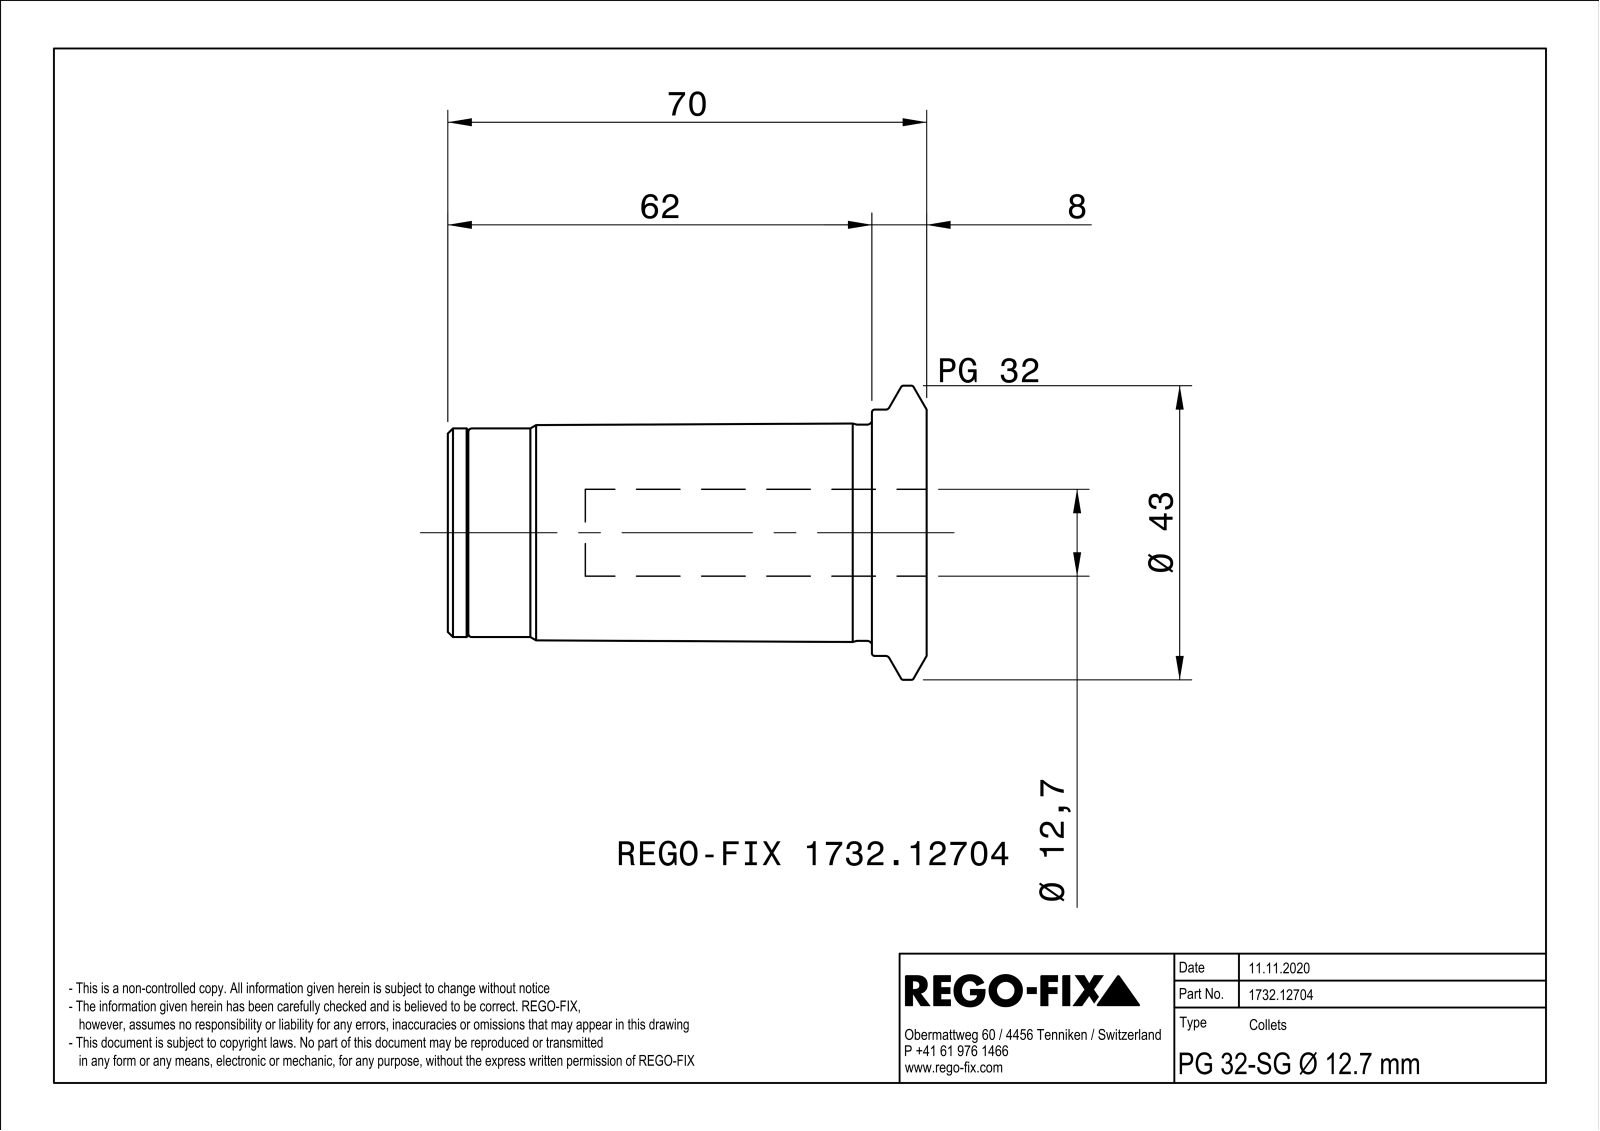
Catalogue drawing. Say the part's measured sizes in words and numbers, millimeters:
The part is named "NOCUT". Its 3-D file was written by "SIEMENS PLM Software Solid Edge ST10 (AUTOMOTIVE_DESIGN)". It is 1 solid with 127 faces: 31 planar, 41 cylindrical and 55 other. Overall it measures 70 by 43 by 42.99 millimeters. Its volume is 45 037 cubic millimeters and its surface area 16 567 square millimeters. Round holes: 3 of diameter 4, 1 of diameter 8.92, 1 of diameter 10.5, 1 of diameter 12.7, 1 of diameter 15.5, 1 of diameter 26.92, 1 of diameter 28.5. Round bosses or shafts: 1 of diameter 43, 1 of diameter 36, 1 of diameter 31.6, 1 of diameter 30.5, 1 of diameter 26.5, 1 of diameter 21. Partial cylindrical surfaces (rounded edges, fillets, slot ends): 6 of radius 2, 3 of radius 3.5, 1 of radius 3.98, 1 of radius 4.75, 1 of radius 8.75. The main face-to-face distances are 1, 70, 58, 12, 59, 11, 8, 60, 2, 10. The hole center spacings are 7.75, 13.42, 13.43.
